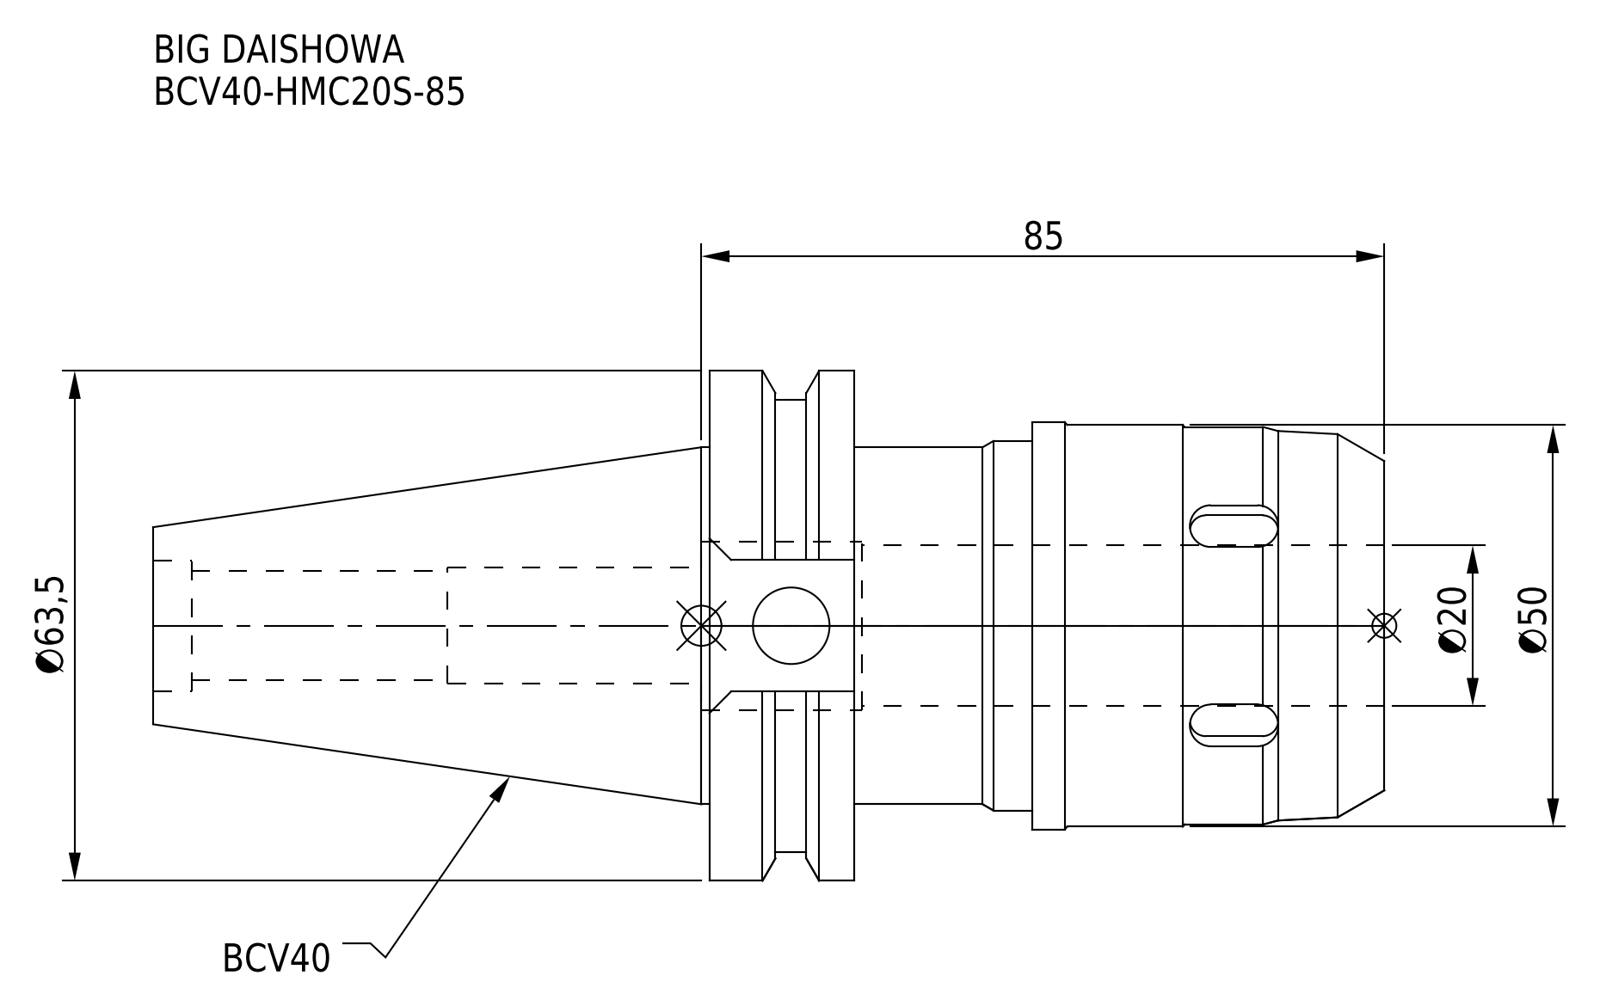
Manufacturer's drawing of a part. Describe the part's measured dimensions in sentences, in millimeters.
The part is named "BCV40-HMC20S-85". Its 3-D file was written by "CREO PARAMETRIC BY PTC INC, 2016380 (AUTOMOTIVE_DESIGN)". It is 1 solid with 106 faces: 42 planar, 42 cylindrical and 22 other. Overall it measures 153.25 by 63.5 by 61.35 millimeters. Its volume is 195 039 cubic millimeters and its surface area 35 723 square millimeters. Round holes: 1 of diameter 9.53, 1 of diameter 13.6, 1 of diameter 14.5, 1 of diameter 16.32, 1 of diameter 20, 1 of diameter 21. Round bosses or shafts: 1 of diameter 63.5, 1 of diameter 56.36, 1 of diameter 50.7, 1 of diameter 50, 1 of diameter 49.5, 1 of diameter 46, 1 of diameter 44.45. Partial cylindrical surfaces (rounded edges, fillets, slot ends): 6 of radius 3. The main face-to-face distances are 18.05, 65.95, 84, 43.8, 22.15, 40.2, 153.25, 109.45, 87.3, 69.25.
